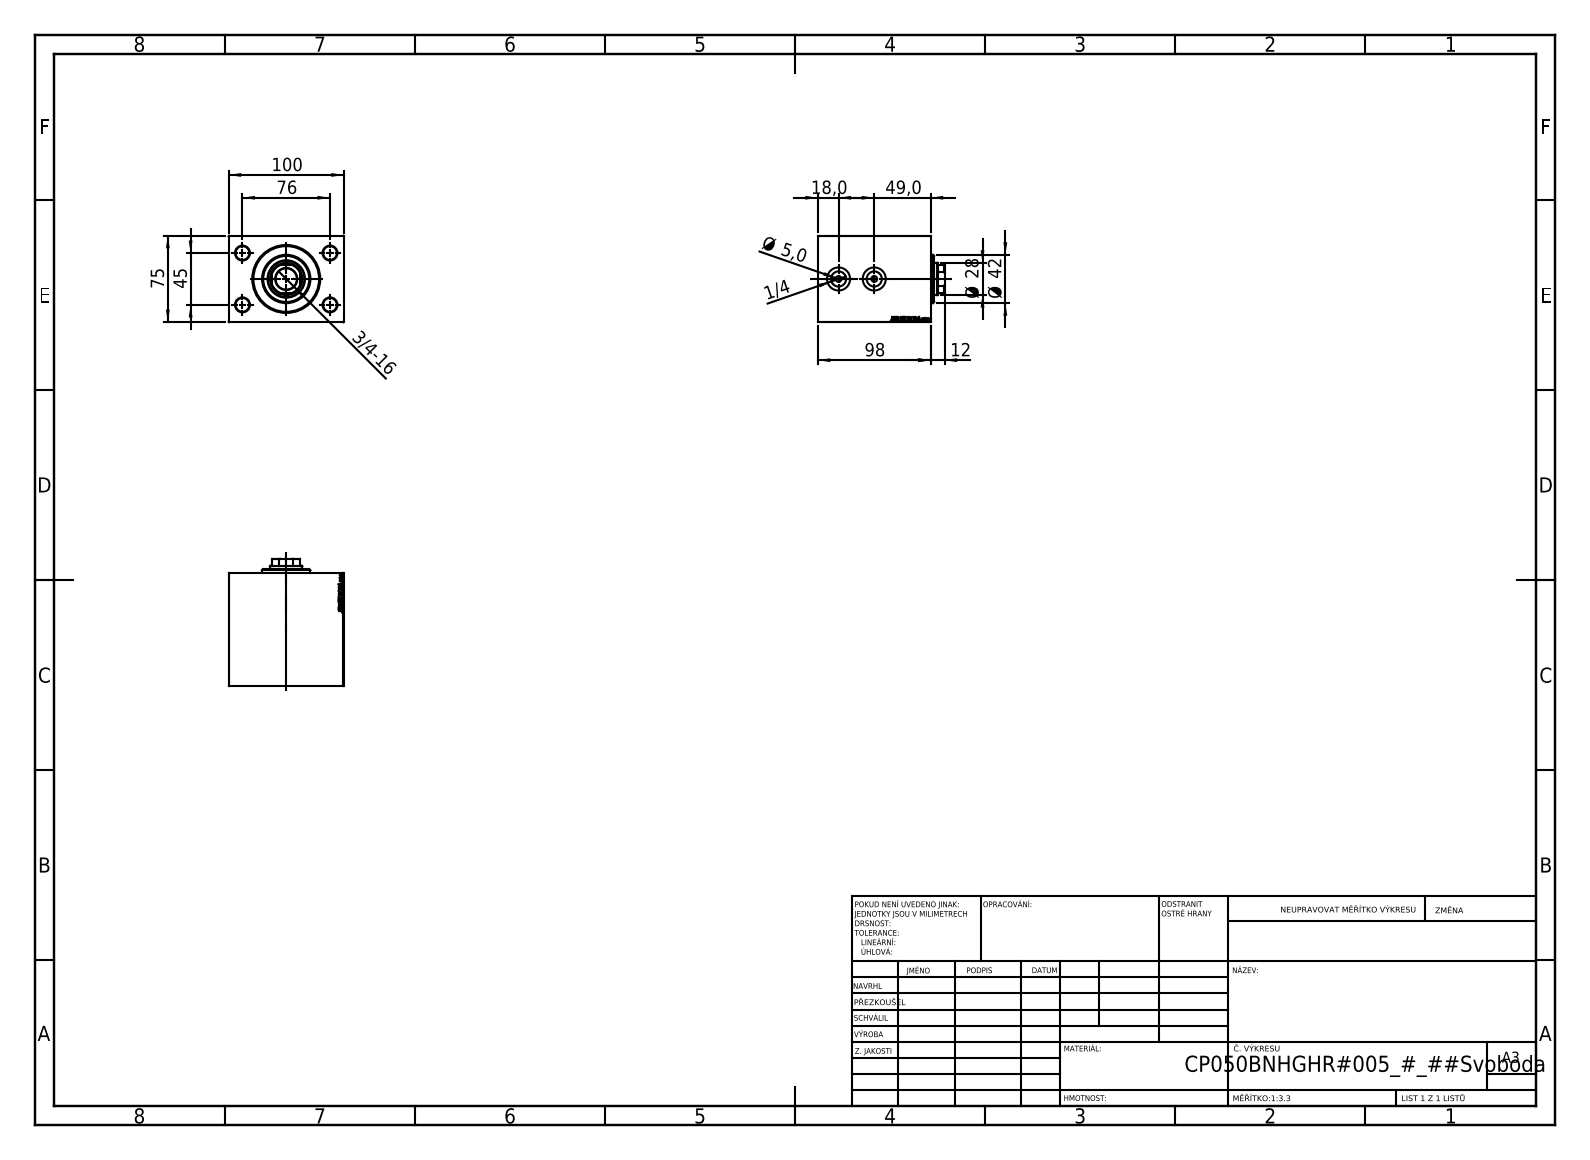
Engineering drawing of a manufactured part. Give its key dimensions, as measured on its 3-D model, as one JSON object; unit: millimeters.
{"part_name": "V450CP_B; V450CP_B_VCP; V450CP_VC_B", "step_written_by": "SolidWorks 2019 (CONFIG_CONTROL_DESIGN)", "units": "millimeters", "bodies": {"solids": 3, "faces": 904, "planar": 406, "cylindrical": 68, "other": 430}, "overall_size": [110, 100, 75], "volume_mm3": 705053, "surface_area_mm2": 103585, "round_holes": [[12, 4], [4, 2], [5, 2], [9.73, 2], [13.16, 2], [15, 2], [20, 2], [18.5, 1], [28, 1], [31.5, 1], [32.5, 1], [50, 1]], "round_bosses_or_shafts": [[42, 1]], "partial_cylinders_radius": [[13.5, 1]], "face_to_face_distances": [75, 100, 98, 49, 14, 84, 44, 5, 35, 30], "hole_center_spacings": [44.16, 45, 76, 88.32, 31, 42.55]}
